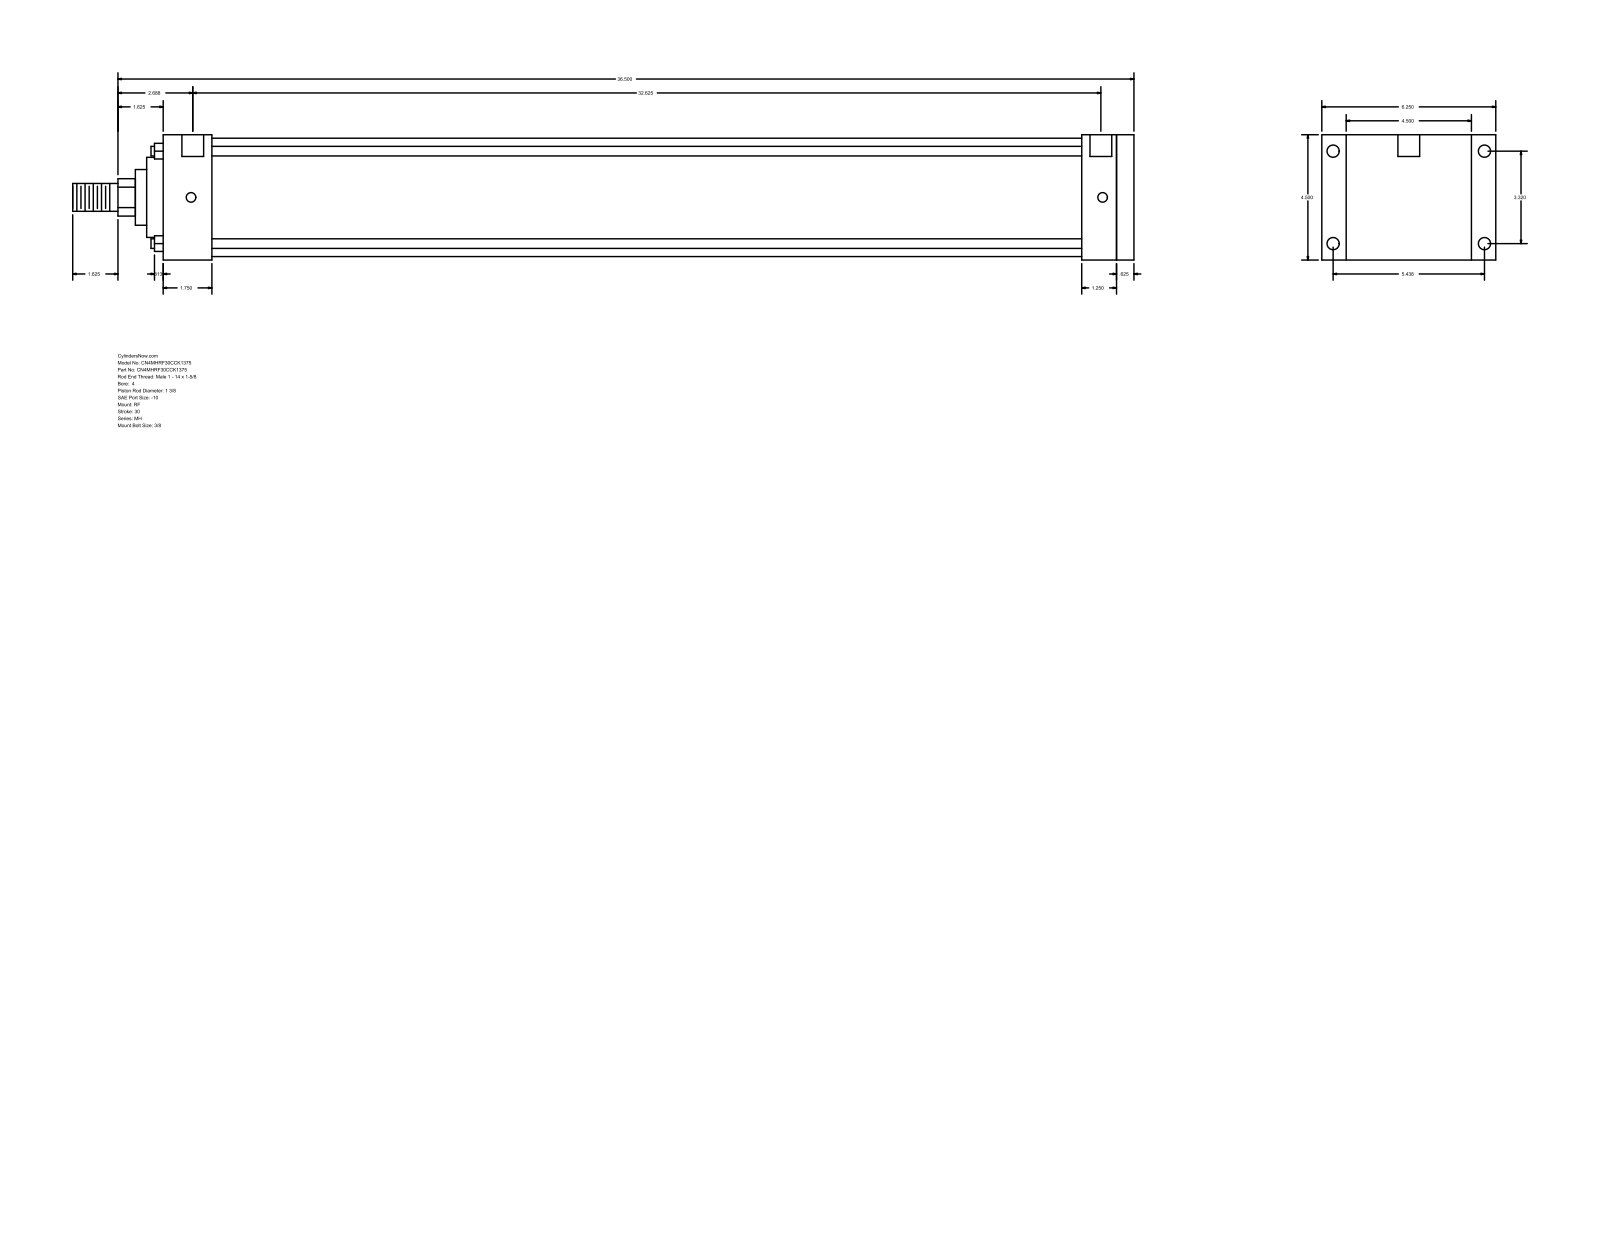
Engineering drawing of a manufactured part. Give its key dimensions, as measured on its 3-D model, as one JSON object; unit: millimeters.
{"part_name": "MH_RF__0400_1.375", "step_written_by": "GSSL Pune (CONFIG_CONTROL_DESIGN)", "units": "millimeters", "bodies": {"solids": 0, "faces": 94, "planar": 65, "cylindrical": 29, "other": 0}, "overall_size": [968.38, 158.75, 114.3], "round_holes": [[8.73, 4], [11.13, 4], [19.84, 2]], "round_bosses_or_shafts": [[8.76, 4], [107.95, 1], [73.03, 1], [50.8, 1], [34.92, 1], [25.4, 1]], "partial_cylinders_radius": [[17.06, 1]], "face_to_face_distances": [114.3, 885.83, 869.96, 15.87, 44.45, 825.51, 841.38, 838.21, 793.76, 31.75], "hole_center_spacings": [84.32, 138.12, 161.82, 831.85, 1.58, 1.59, 828.68, 830.26]}
